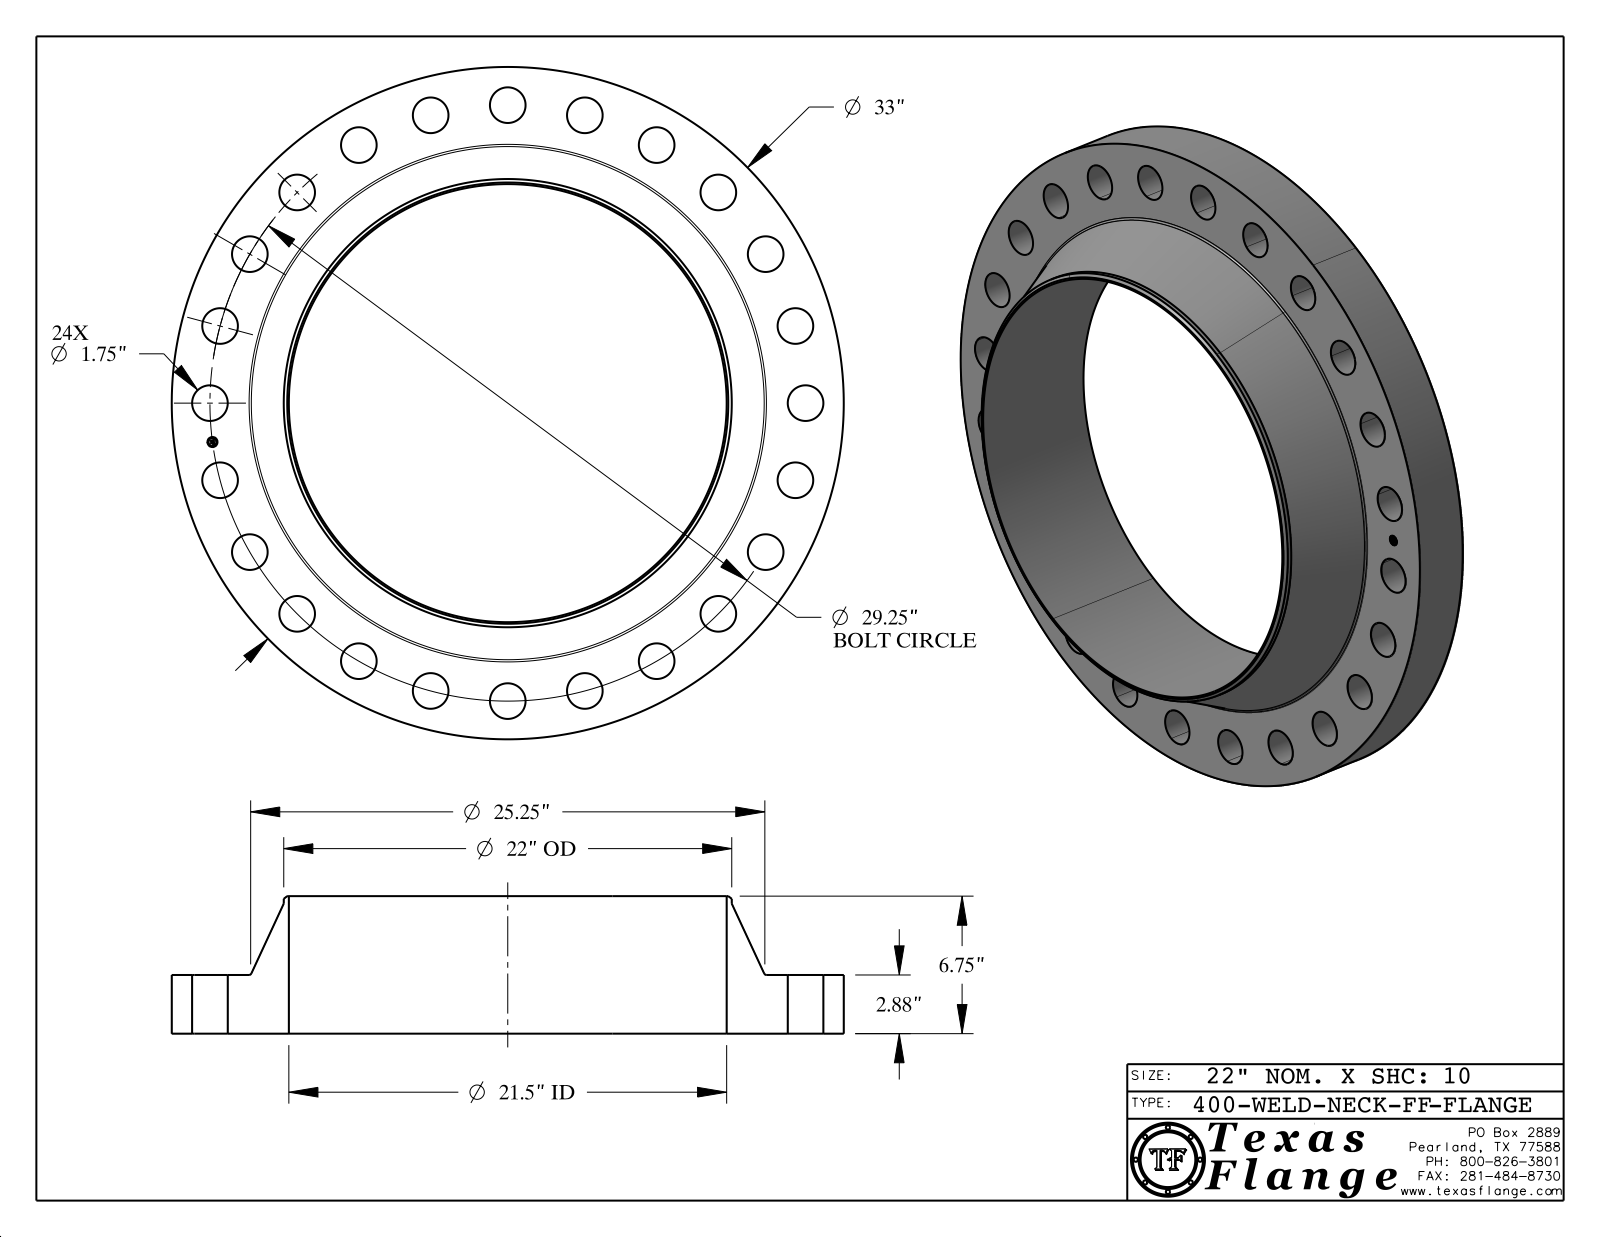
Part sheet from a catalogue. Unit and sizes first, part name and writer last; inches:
Units: inches
Overall size (bounding box): 33 × 33 × 6.75
Round holes (diameter × count): ⌀1.75 ×24, ⌀0.495 ×1, ⌀21.5 ×1
Round bosses / shafts (diameter × count): ⌀0.03 ×8, ⌀33 ×1, ⌀22 ×1, ⌀0.39 ×1
Main face-to-face distances: 2.88, 6.75, 3.87, 2.865, 0.015, 3.885, 0.148, 0.145, 0.027, 0.096
Hole centre spacings: 14.625, 27.024, 7.57, 20.683, 3.818, 11.194, 17.806, 23.206
Volume: 1 523 in³ · Surface area: 2 188 in²
Bodies: 1 solid, 448 faces (368 planar, 74 cylindrical, 6 other)
Part name (STEP PRODUCT): 400-WELD-NECK-FF
STEP written by: CATIA V5 STEP AP214 (AUTOMOTIVE_DESIGN)
